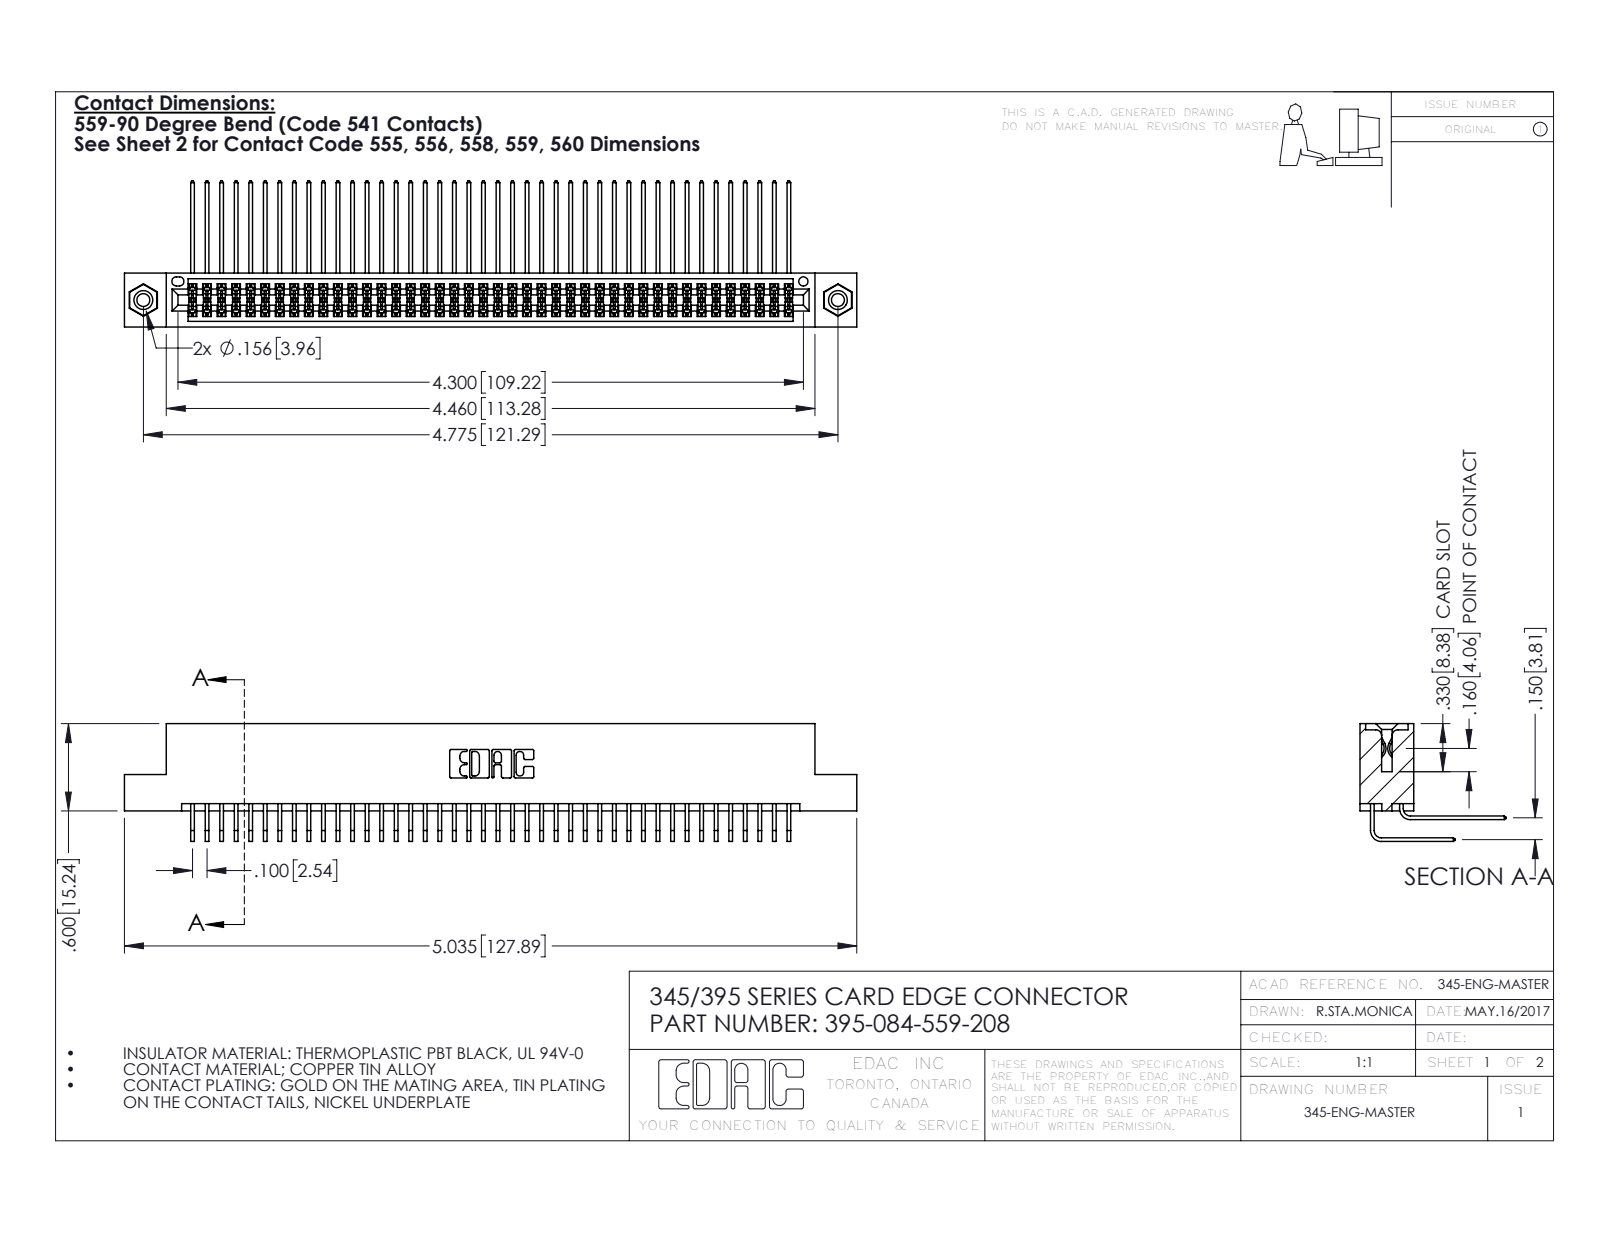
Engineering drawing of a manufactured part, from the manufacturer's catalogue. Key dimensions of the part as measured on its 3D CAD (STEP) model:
Part name (STEP PRODUCT): 345 Part_Flush Mounting Lugs - 0.156 Dia-TI; 395-084-559-208; 345-292-001_558 559 Tail - 1; 345-250-001_345-250-003-102 (+1 more)
STEP written by: SolidWorks 2016 (CONFIG_CONTROL_DESIGN)
Units: inches
Bodies: 87 solids, 4554 faces (3052 planar, 1486 cylindrical, 16 other)
Overall size (bounding box): 5.035 × 1.005 × 0.809
Volume: 0.787 in³ · Surface area: 33.11 in²
Round holes (diameter × count): ⌀0.089 ×2, ⌀0.125 ×2, ⌀0.156 ×2, ⌀0.064 ×1
Round bosses / shafts (diameter × count): ⌀0.155 ×2
Partial cylindrical surfaces — rounded edges, fillets, slot ends (radius × count): R0.006 ×126, R0.01 ×22, R0.007 ×6, R0.031 ×6, R0.026 ×3, R0.014 ×2, R0.019 ×2, R0.022 ×2
Main face-to-face distances: 0.072, 0.298, 0.2, 0.37, 0.098, 0.272, 0.025, 0.225, 0.175, 0.15
Hole centre spacings: 0.27, 4.539, 4.775
